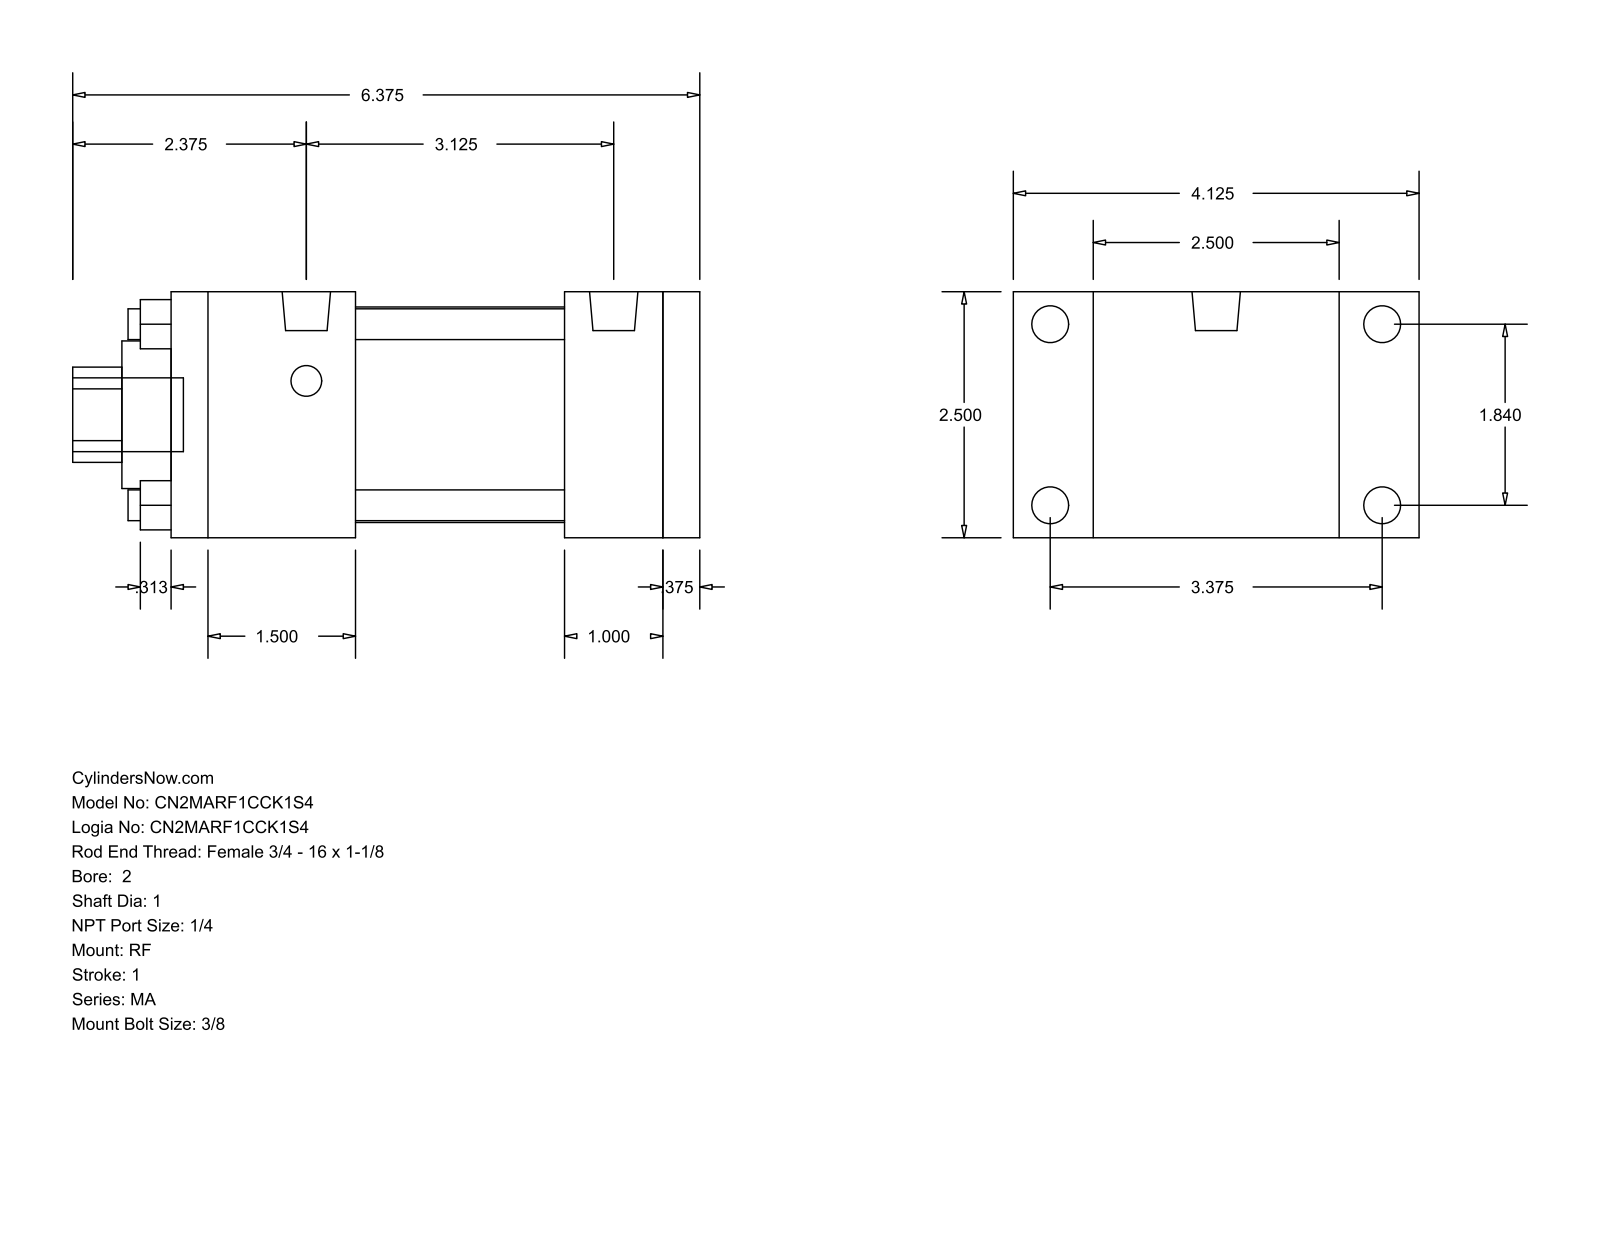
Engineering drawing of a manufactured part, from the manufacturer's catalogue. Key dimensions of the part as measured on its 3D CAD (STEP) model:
Part name (STEP PRODUCT): MA_RF__0200_1
STEP written by: GSSL Pune (CONFIG_CONTROL_DESIGN)
Units: millimetres
Bodies: 0 solids, 92 faces (64 planar, 28 cylindrical, 0 other)
Overall size (bounding box): 161.93 × 104.78 × 63.5
Round holes (diameter × count): ⌀7.94 ×4, ⌀25.4 ×1, ⌀38.1 ×1, ⌀55.63 ×1
Round bosses / shafts (diameter × count): ⌀9.53 ×4, ⌀7.94 ×4, ⌀12.49 ×2, ⌀19.05 ×1
Partial cylindrical surfaces — rounded edges, fillets, slot ends (radius × count): R12.29 ×1
Main face-to-face distances: 63.5, 127, 9.53, 136.53, 25.4, 20.64, 12.7, 47.63, 79.37, 88.9
Hole centre spacings: 33.05, 46.74, 66.1
